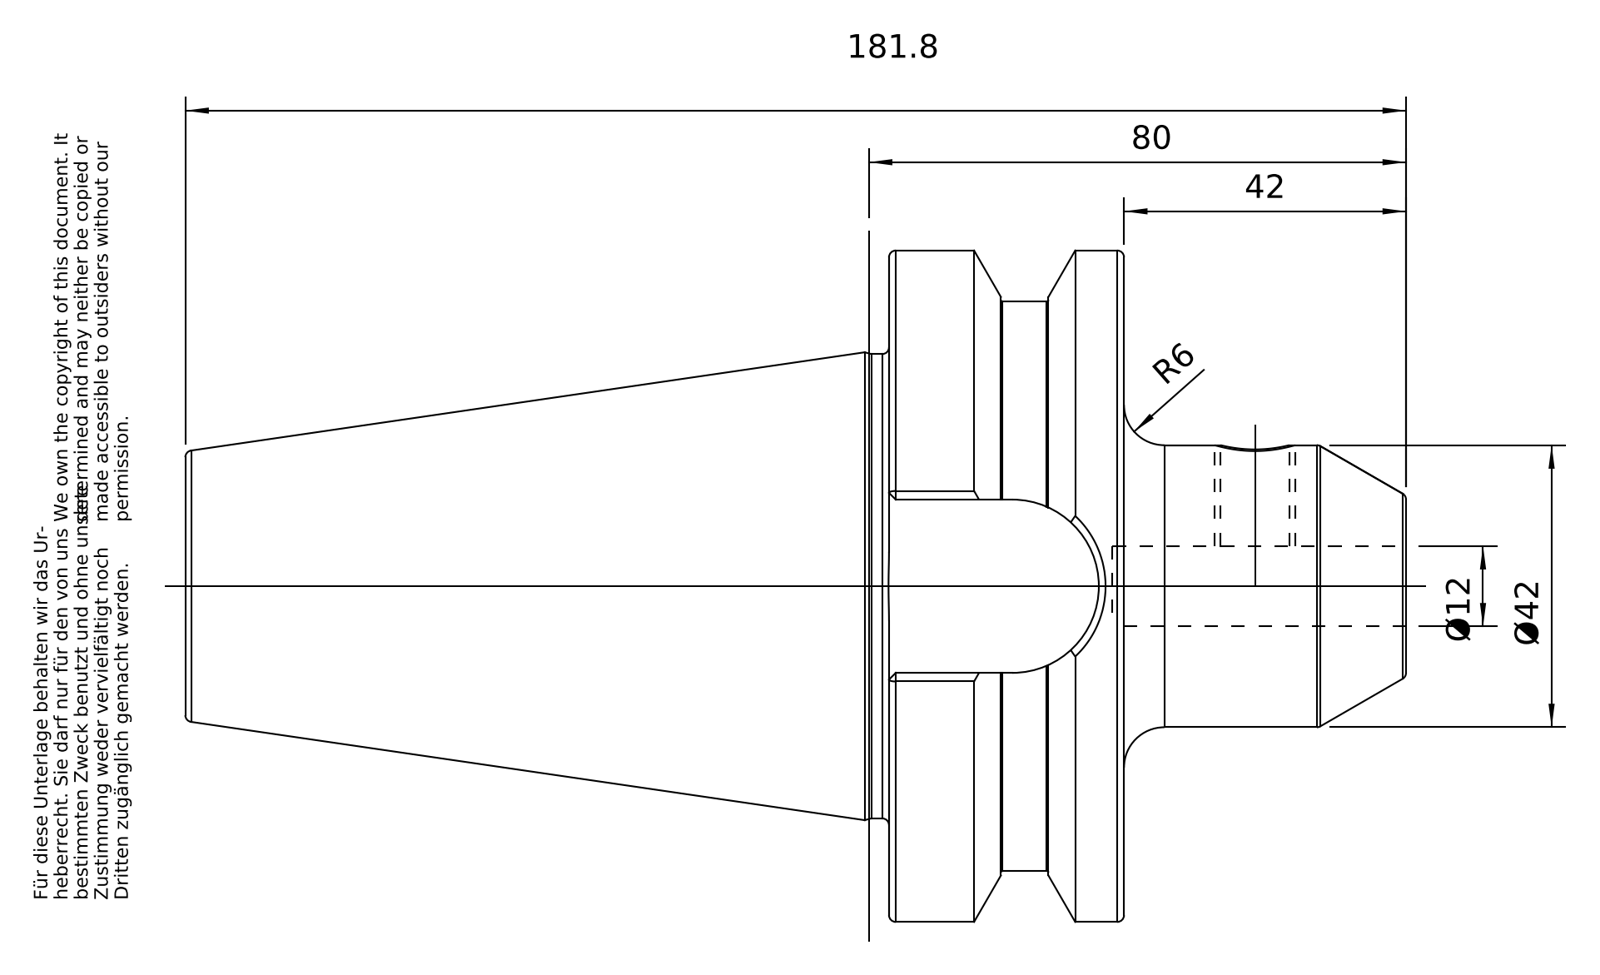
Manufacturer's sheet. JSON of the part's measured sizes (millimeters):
{"part_name": "50-500-12", "step_written_by": "PRO/ENGINEER BY PARAMETRIC TECHNOLOGY CORPORATION, 2010430 (CONFIG_CONTROL_DESIGN)", "units": "millimeters", "bodies": {"solids": 1, "faces": 102, "planar": 26, "cylindrical": 26, "other": 50}, "overall_size": [181.8, 99.97, 99.97], "volume_mm3": 515438, "surface_area_mm2": 58770, "round_holes": [[12, 2], [10.2, 1], [20.75, 1], [25.02, 1], [25.7, 1]], "round_bosses_or_shafts": [[99.97, 1], [84.75, 1], [69.15, 1], [42, 1], [24.01, 1]], "partial_cylinders_radius": [[12.9, 1]], "face_to_face_distances": [35, 70.4, 104.8, 139.8, 181.8, 77, 42, 25.8, 48, 56.8]}
